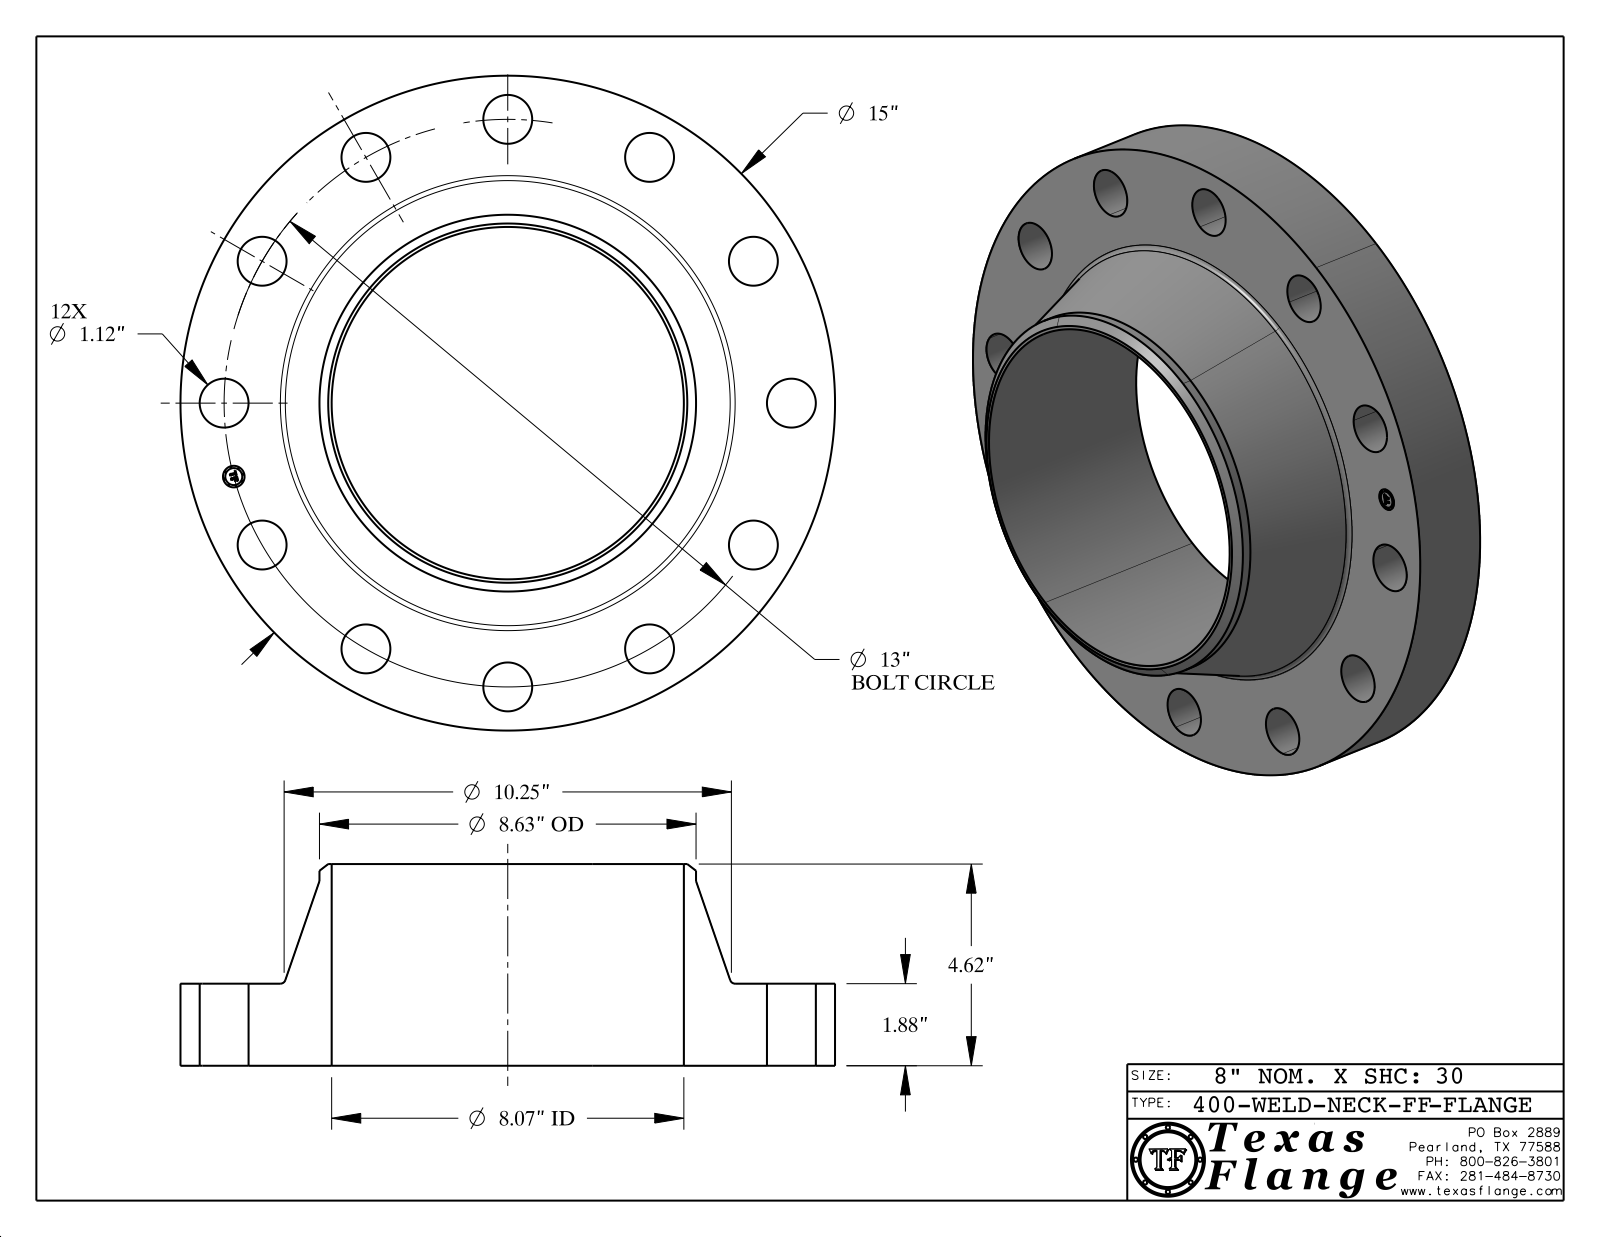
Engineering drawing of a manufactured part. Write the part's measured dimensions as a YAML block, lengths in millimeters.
part_name: "400-WELD-NECK-FF"
step_written_by: "CATIA V5 STEP AP214 (AUTOMOTIVE_DESIGN)"
units: millimeters
bodies: {solids: 1, faces: 424, planar: 368, cylindrical: 50, other: 6}
overall_size: [381, 381, 117.3]
volume: 4275000
surface_area: 367400
round_holes:
  - {diameter: 28.4, count: 12}
  - {diameter: 12.6, count: 1}
  - {diameter: 205, count: 1}
round_bosses_or_shafts:
  - {diameter: 0.8, count: 8}
  - {diameter: 381, count: 1}
  - {diameter: 219.2, count: 1}
  - {diameter: 9.9, count: 1}
face_to_face_distances: [47.8, 117.3, 69.6, 47.4, 0.4, 70, 3.8, 3.7, 0.7, 2.4]
hole_center_spacings: [165.1, 85.5, 233.5, 286, 318.9, 330.2, 43.1, 126.4]
